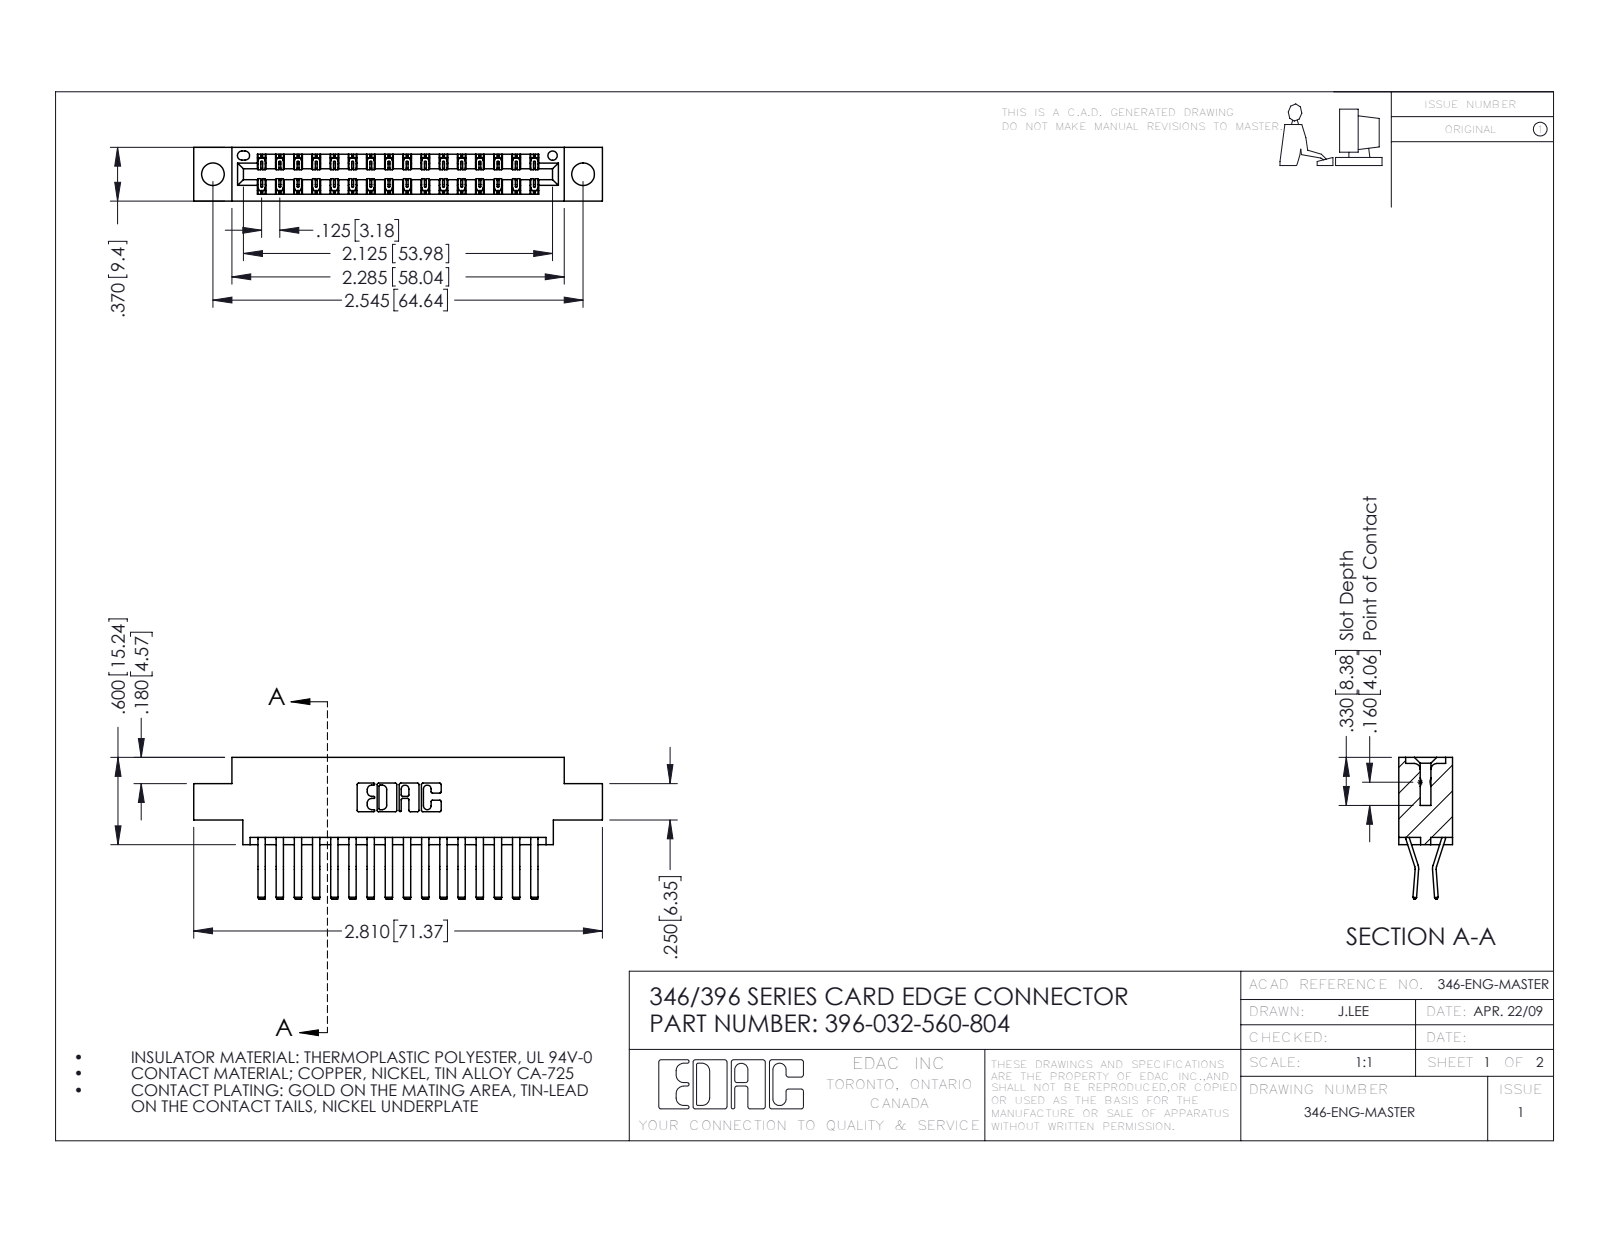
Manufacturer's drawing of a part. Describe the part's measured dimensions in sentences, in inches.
The part is named "346 Part_0.170 Offset - 0.156 Dia-TH; 345-292-001_560 Tail; 396-032-560-804". Its 3-D file was written by "SolidWorks 2016 (CONFIG_CONTROL_DESIGN)". It is 33 solids with 1854 faces: 1200 planar, 654 cylindrical and 0 other. Overall it measures 2.81 by 0.975 by 0.37 inches. Its volume is 0.41 cubic inches and its surface area 14.55 square inches. Round holes: 2 of diameter 0.156, 1 of diameter 0.064. Partial cylindrical surfaces (rounded edges, fillets, slot ends): 48 of radius 0.006, 22 of radius 0.01, 6 of radius 0.007, 6 of radius 0.031, 3 of radius 0.026, 2 of radius 0.01, 2 of radius 0.014, 2 of radius 0.022. The main face-to-face distances are 0.048, 0.322, 0.37, 0.25, 0.025, 0.072, 0.298, 0.275, 0.148, 0.222. The hole center spacings are 0.246, 2.338, 2.545.
